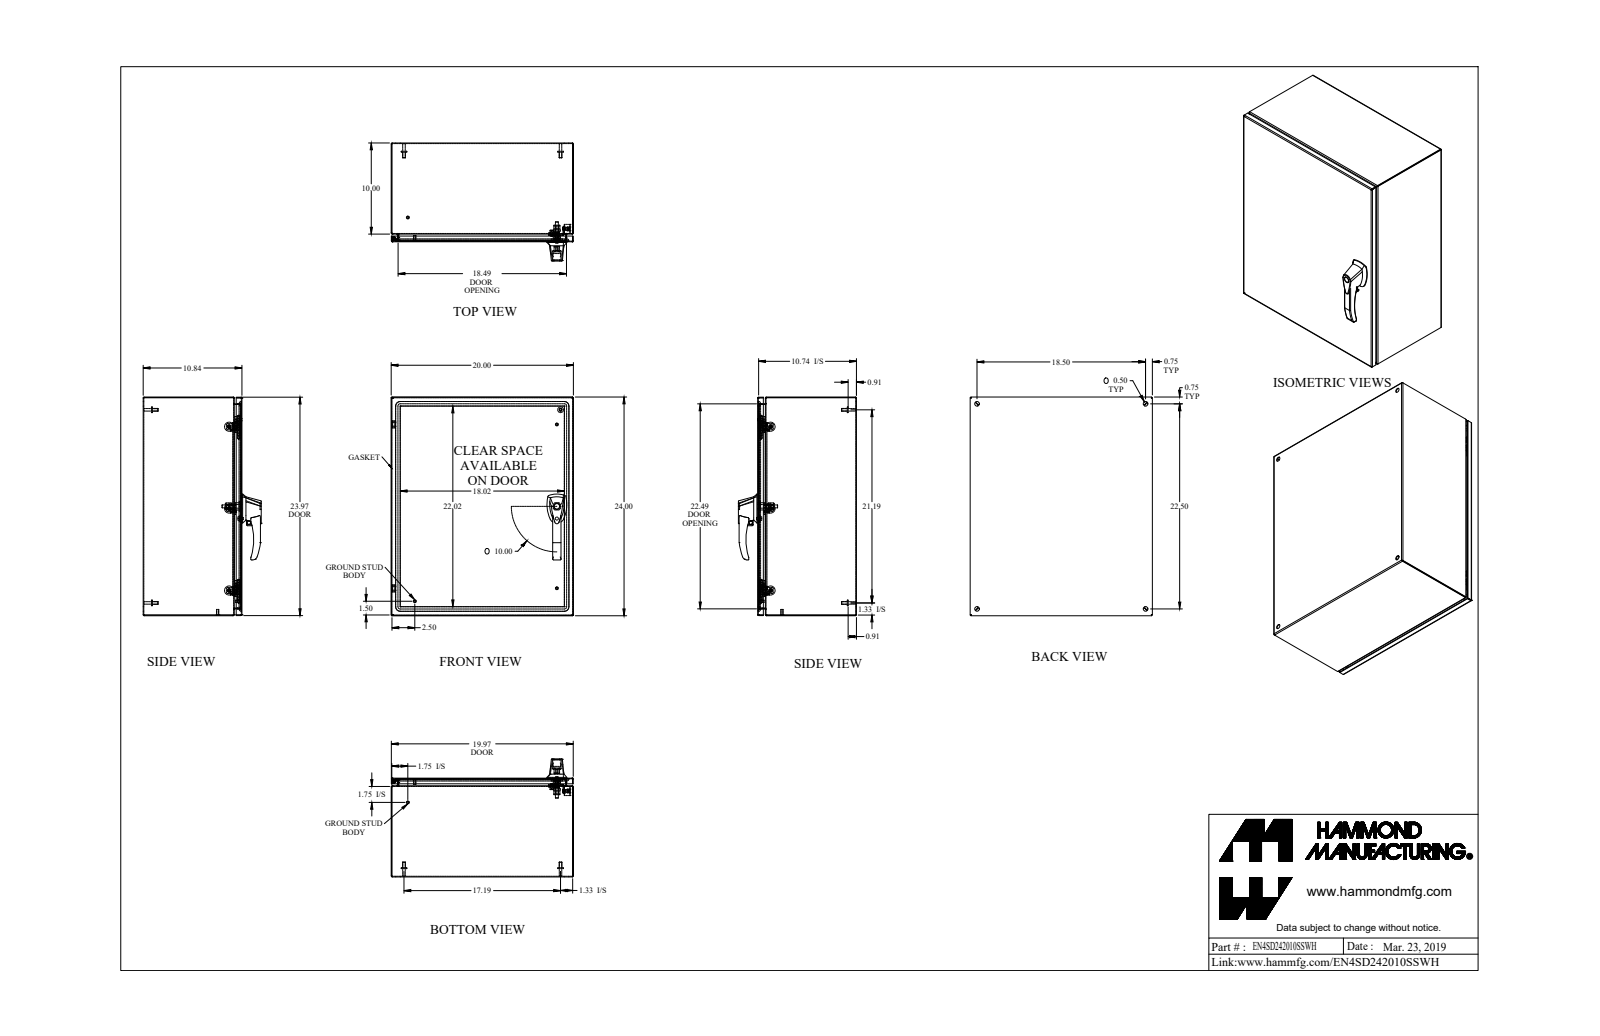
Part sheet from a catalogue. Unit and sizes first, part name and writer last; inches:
Units: inches
Overall size (bounding box): 24 × 20 × 12.958
Round holes (diameter × count): ⌀0.176 ×6, ⌀0.5 ×4, ⌀0.25 ×3, ⌀0.265 ×3, ⌀0.313 ×3, ⌀0.413 ×3, ⌀0.196 ×2, ⌀0.256 ×2, ⌀0.394 ×2, ⌀0.172 ×1, ⌀0.233 ×1, ⌀0.24 ×1
Round bosses / shafts (diameter × count): ⌀0.25 ×7, ⌀0.375 ×6, ⌀0.313 ×6, ⌀0.156 ×6, ⌀0.625 ×4, ⌀0.275 ×4, ⌀1 ×3, ⌀0.51 ×3
Partial cylindrical surfaces — rounded edges, fillets, slot ends (radius × count): R0.036 ×20, R0.108 ×20, R0.25 ×19, R0.125 ×9, R0.06 ×7, R0.03 ×6, R0.09 ×6, R0.006 ×4
Main face-to-face distances: 0.072, 10.771, 10.699, 10.843, 19.928, 23.928, 19.856, 20, 23.856, 24
Hole centre spacings: 2.502, 8.984, 8.985, 8.985, 9, 11.3, 17.585, 17.969
Volume: 167.3 in³ · Surface area: 4 319 in²
Bodies: 46 solids, 1205 faces (522 planar, 467 cylindrical, 216 other)
Part name (STEP PRODUCT): EN4SD242010SSWH_Default
STEP written by: SolidWorks 2019 (CONFIG_CONTROL_DESIGN)
